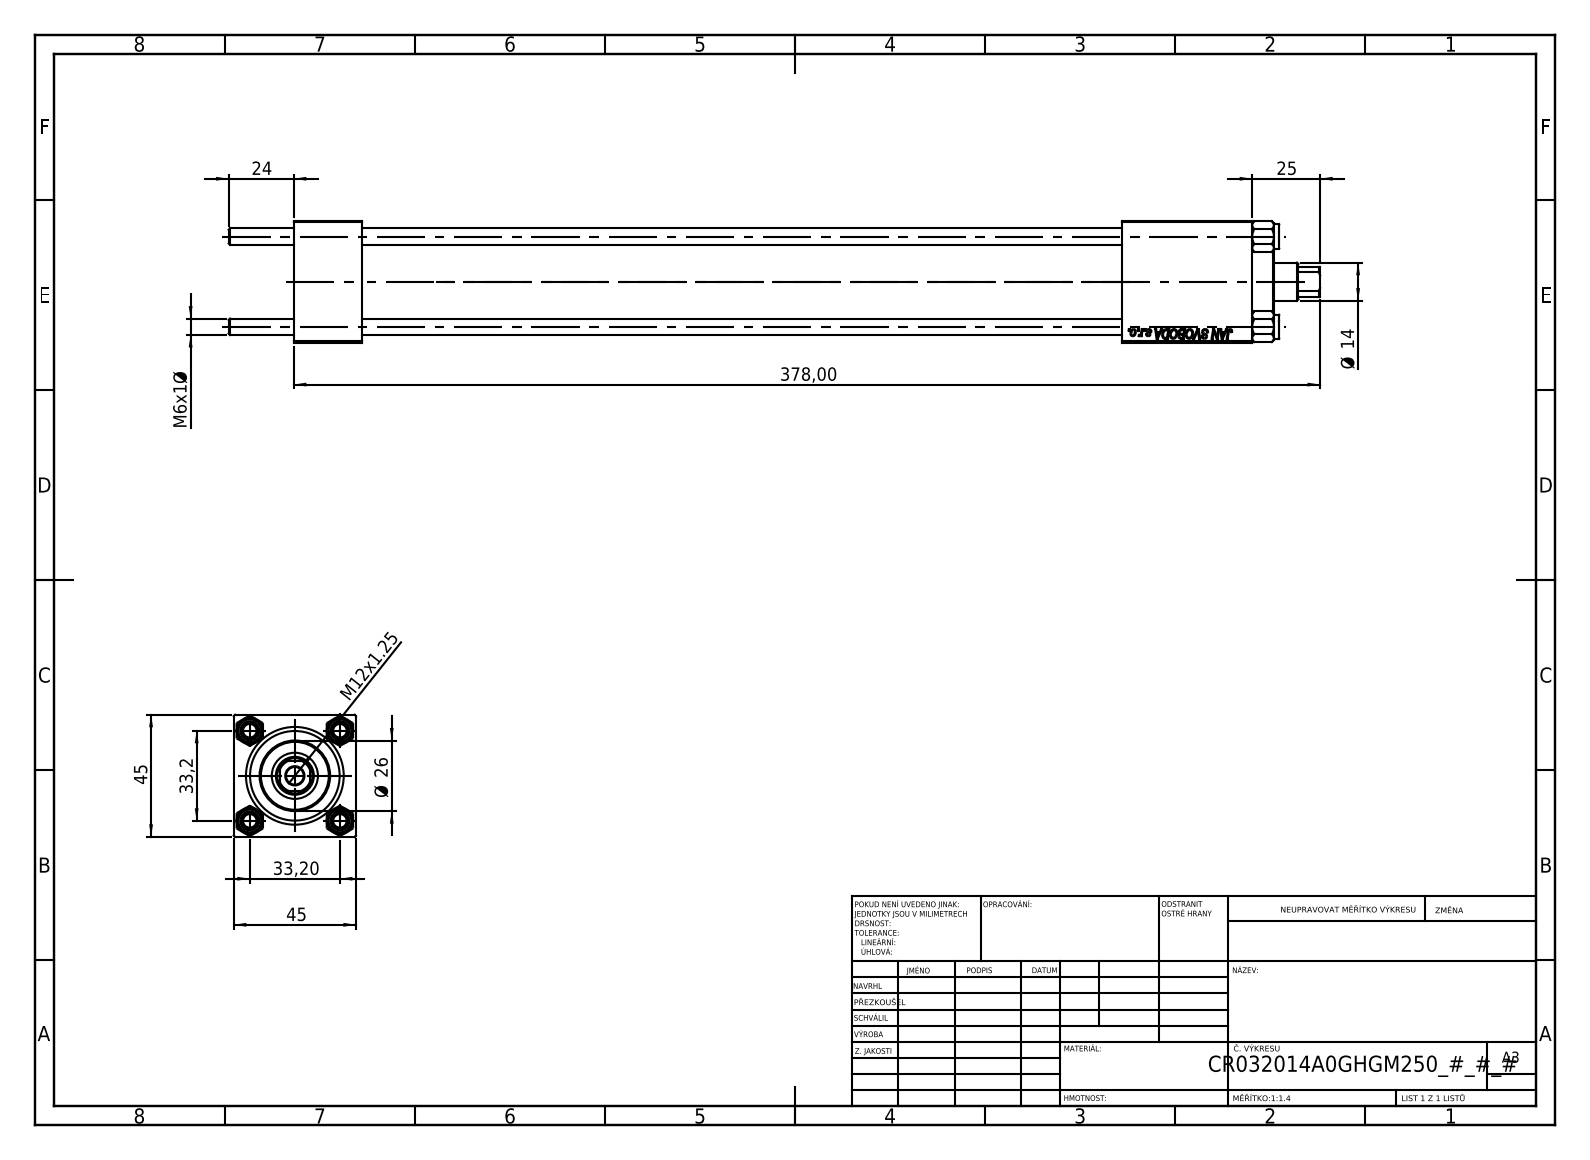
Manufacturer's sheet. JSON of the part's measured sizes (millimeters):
{"part_name": "CR025_012_A_0_G_A_G_M_020_+#_##_TYCINKA; V215_VC_A; NUT_M5; V215CR_VCP (+1 more)", "step_written_by": "SolidWorks 2019 (CONFIG_CONTROL_DESIGN)", "units": "millimeters", "bodies": {"solids": 11, "faces": 1133, "planar": 519, "cylindrical": 78, "other": 536}, "overall_size": [402, 45, 45], "volume_mm3": 335599, "surface_area_mm2": 150861, "round_holes": [[6, 4], [7, 2], [13.16, 2], [20, 2], [6.5, 1], [14, 1], [17, 1], [24, 1], [32, 1], [33, 1]], "round_bosses_or_shafts": [[9, 4], [38, 1], [26, 1]], "partial_cylinders_radius": [[6.5, 1]], "face_to_face_distances": [45, 25, 353, 328, 305, 280, 48, 324.3, 299.3, 19.3], "hole_center_spacings": [23.48, 33.2, 46.95, 305.5]}
